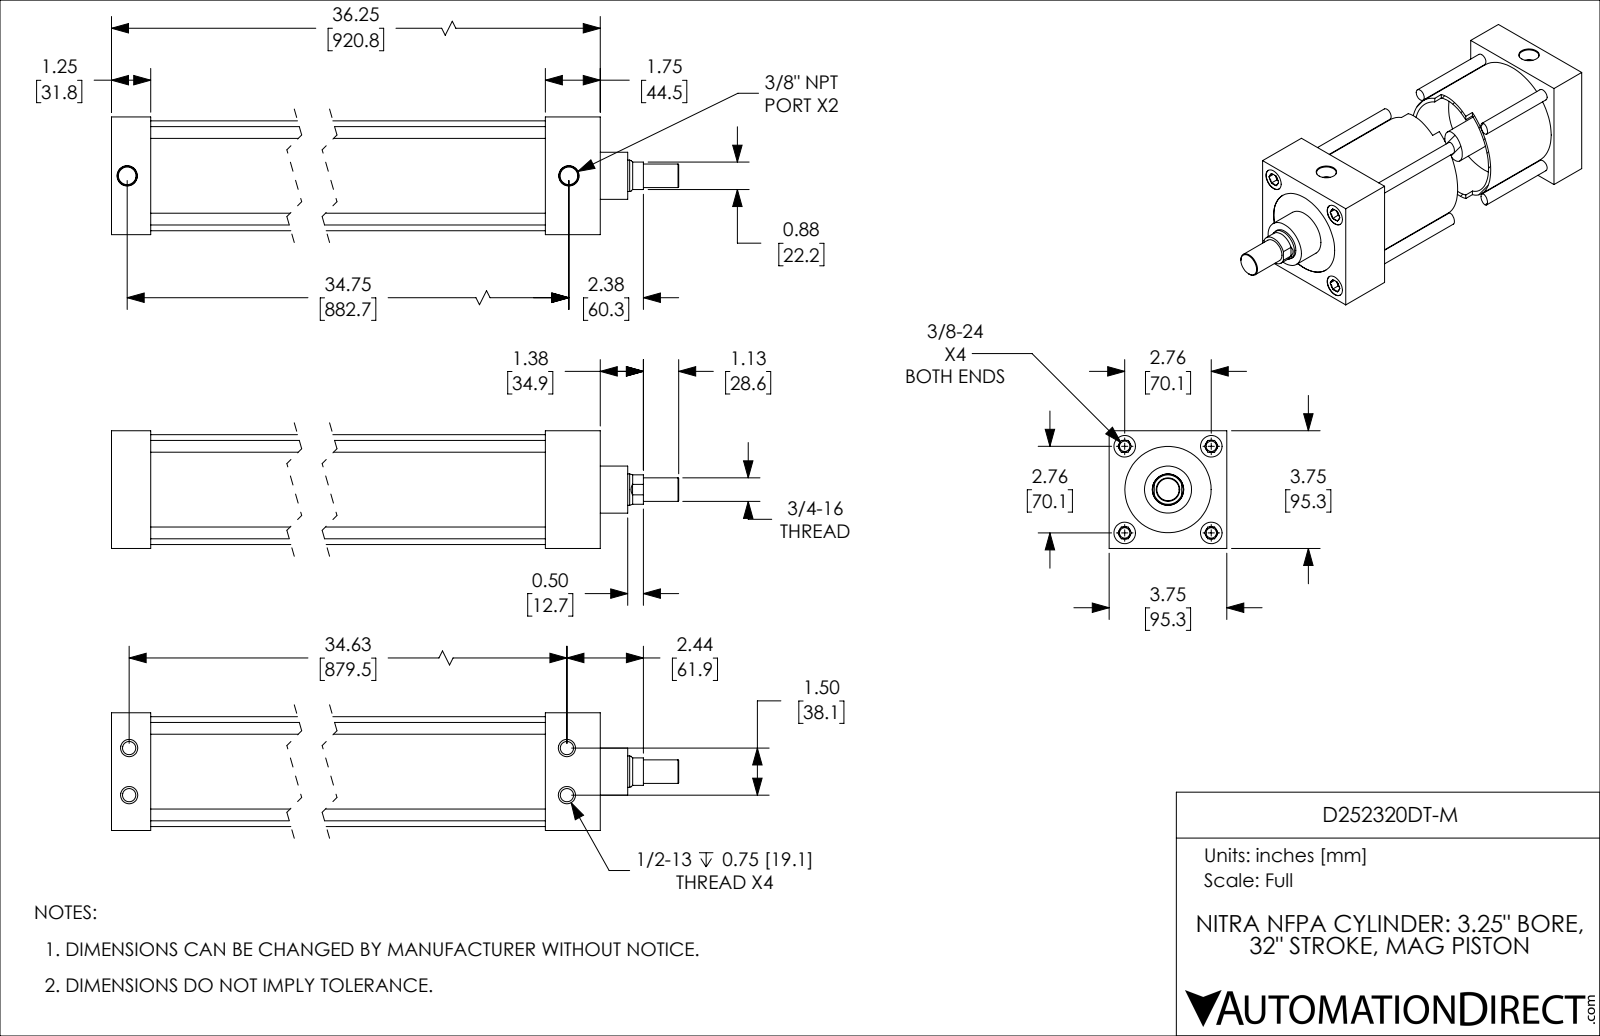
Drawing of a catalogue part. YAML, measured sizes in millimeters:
part_name: "D252320DT-M_BODY; D252320DT-M_PISTON_KK1; D252320DT-M"
step_written_by: "SolidWorks 2019 (CONFIG_CONTROL_DESIGN)"
units: millimeters
bodies: {solids: 2, faces: 198, planar: 58, cylindrical: 62, other: 78}
overall_size: [984.3, 95.3, 95.3]
volume: 2238000
surface_area: 729700
round_holes:
  - {diameter: 8.4, count: 4}
  - {diameter: 10.7, count: 4}
  - {diameter: 17.4, count: 4}
  - {diameter: 14.3, count: 2}
  - {diameter: 25.4, count: 1}
  - {diameter: 69.9, count: 1}
  - {diameter: 82.6, count: 1}
round_bosses_or_shafts:
  - {diameter: 9.5, count: 4}
  - {diameter: 88.9, count: 1}
  - {diameter: 82.5, count: 1}
  - {diameter: 38.1, count: 1}
  - {diameter: 25.4, count: 1}
  - {diameter: 19.1, count: 1}
partial_cylinders:
  - {radius: 11.9, count: 1}
face_to_face_distances: [31.8, 95.3, 876.3, 844.6, 63.5, 812.8, 920.8, 889, 857.3, 44.5]
hole_center_spacings: [19.1, 49.6, 70.1, 881.3, 38.1, 99.1, 879.5, 880.3]
